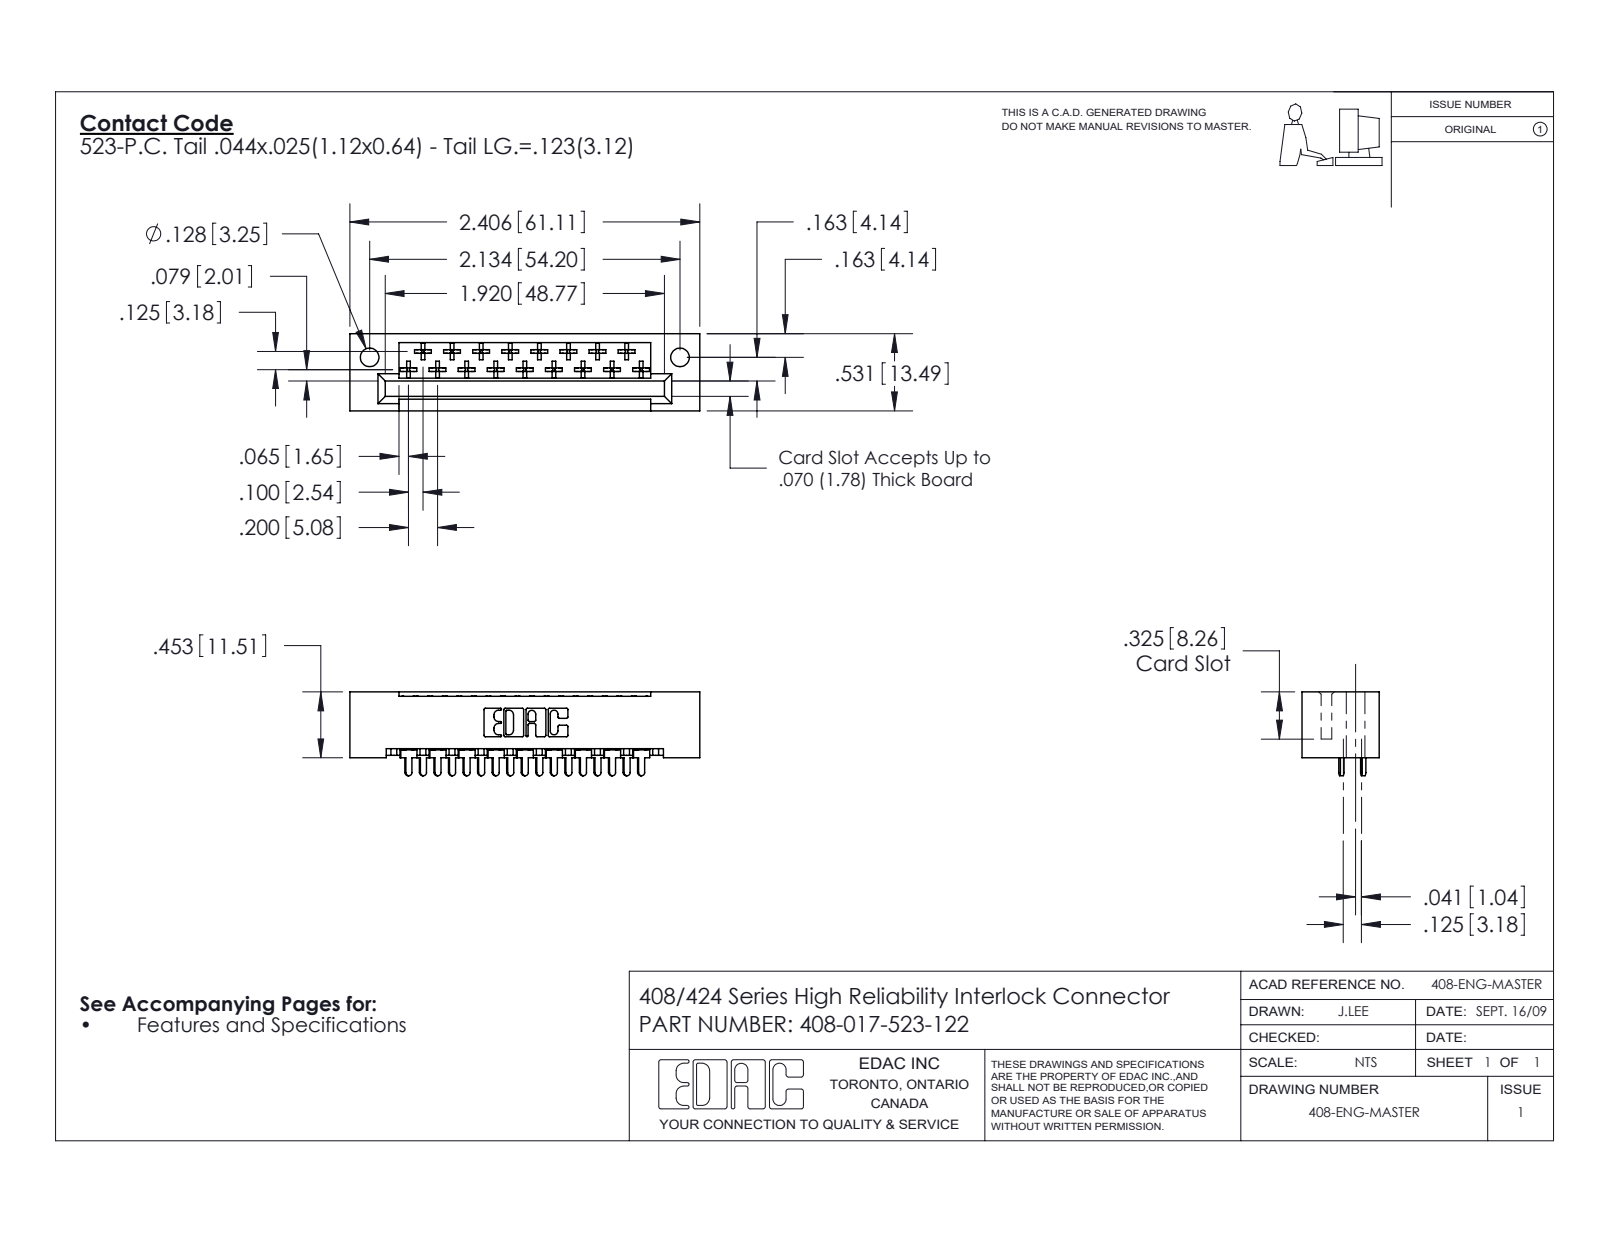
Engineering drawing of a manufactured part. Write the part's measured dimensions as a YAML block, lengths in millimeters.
part_name: "408-290-001_408-290-123 - Top; 408-017-523-122; 408 Part_017 - 1; 408-290-001_408-290-123 - Bottom"
step_written_by: "SolidWorks 2016 (CONFIG_CONTROL_DESIGN)"
units: millimeters
bodies: {solids: 18, faces: 1062, planar: 793, cylindrical: 201, other: 68}
overall_size: [61.1, 14.6, 13.5]
volume: 6870
surface_area: 7865
round_holes:
  - {diameter: 3.3, count: 2}
partial_cylinders:
  - {radius: 0.3, count: 102}
  - {radius: 0.3, count: 22}
  - {radius: 0.5, count: 19}
  - {radius: 0.6, count: 17}
  - {radius: 0.2, count: 6}
  - {radius: 0.8, count: 6}
  - {radius: 0.7, count: 3}
face_to_face_distances: [2.5, 7.5, 0.6, 13.5, 0.6, 3.2, 6.9, 6, 6.6, 5.5]
hole_center_spacings: [54.2]
